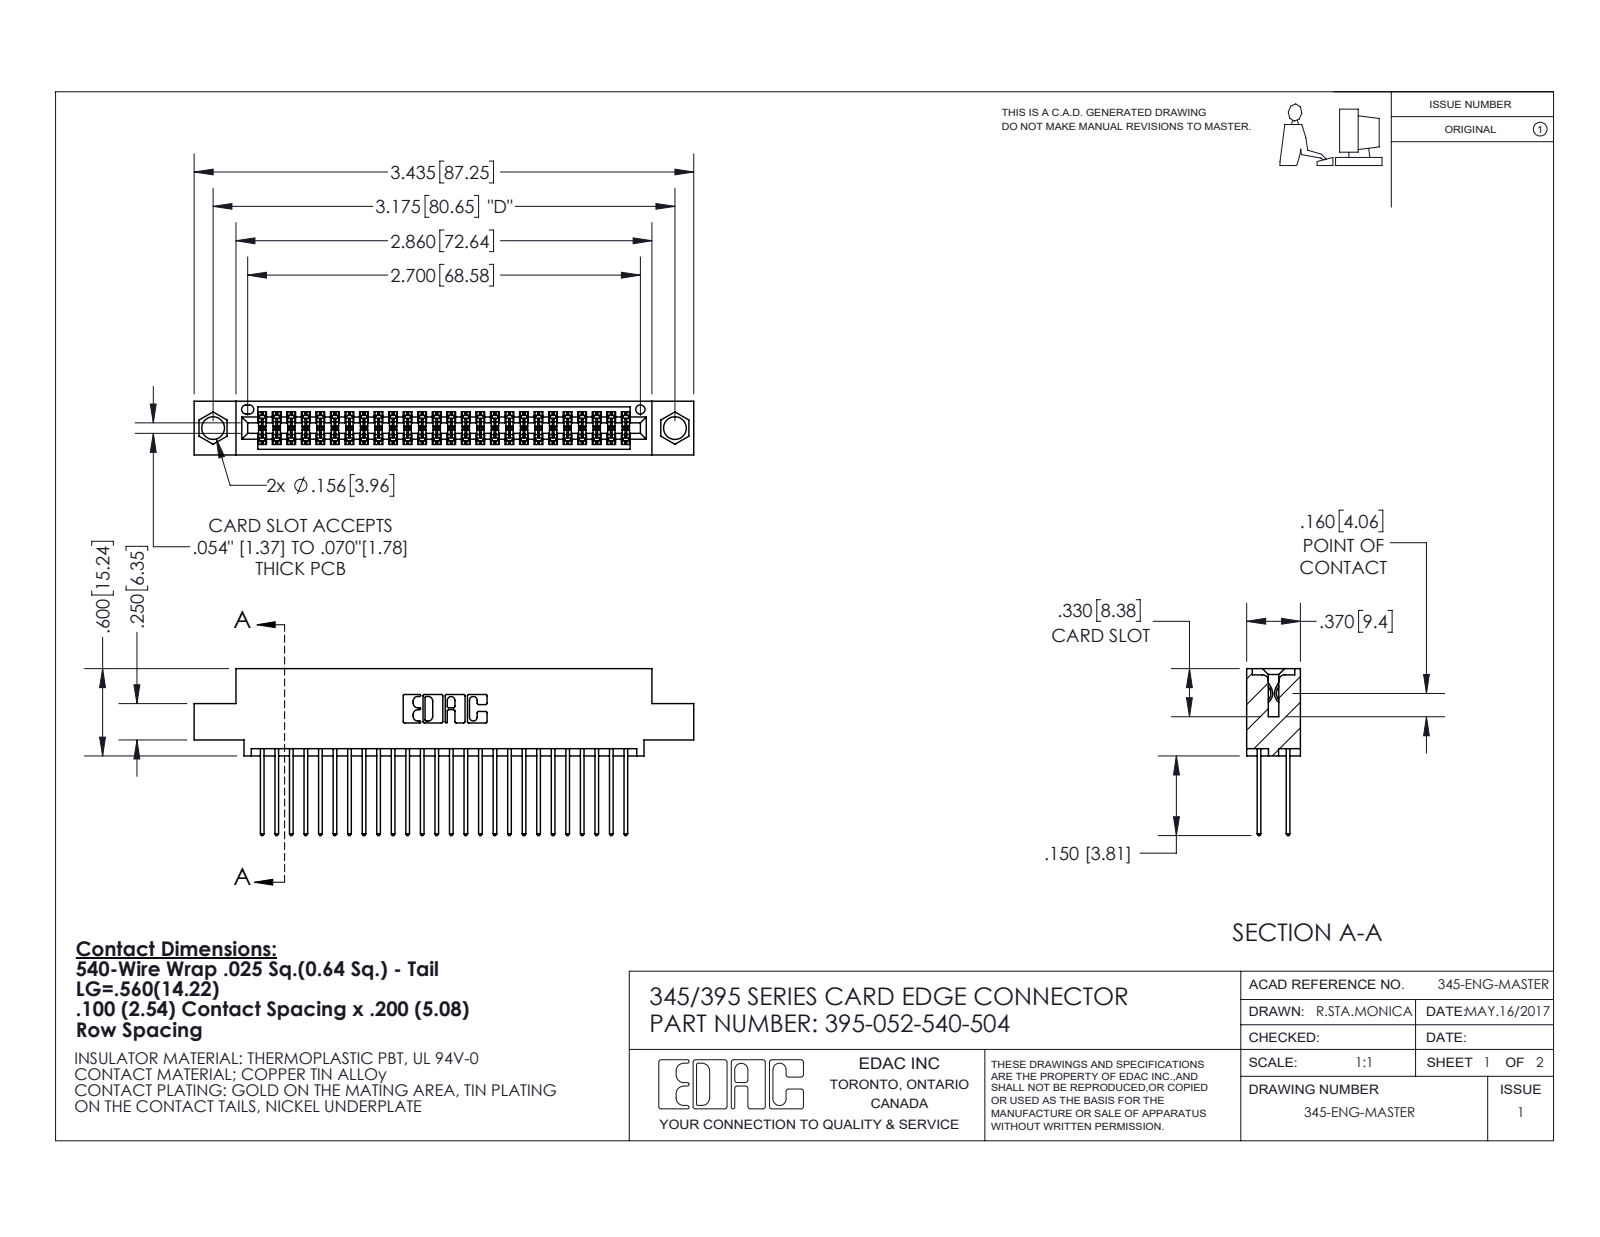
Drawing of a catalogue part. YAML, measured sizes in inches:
part_name: "345 Part_0.110 Offset - 0.156 Dia-TI; 345-292-001_345-293-140; 395-052-540-504"
step_written_by: "SolidWorks 2020 (CONFIG_CONTROL_DESIGN)"
units: inches
bodies: {solids: 53, faces: 2744, planar: 1814, cylindrical: 930, other: 0}
overall_size: [3.435, 1.147, 0.37]
volume: 0.509
surface_area: 19.97
round_holes:
  - {diameter: 0.156, count: 2}
  - {diameter: 0.064, count: 1}
partial_cylinders:
  - {radius: 0.006, count: 104}
  - {radius: 0.01, count: 52}
  - {radius: 0.01, count: 22}
  - {radius: 0.007, count: 6}
  - {radius: 0.031, count: 6}
  - {radius: 0.026, count: 3}
  - {radius: 0.014, count: 2}
  - {radius: 0.019, count: 2}
face_to_face_distances: [0.072, 0.298, 0.2, 0.098, 0.272, 0.025, 0.37, 0.225, 0.175, 0.149]
hole_center_spacings: [0.27, 2.94, 3.175]
